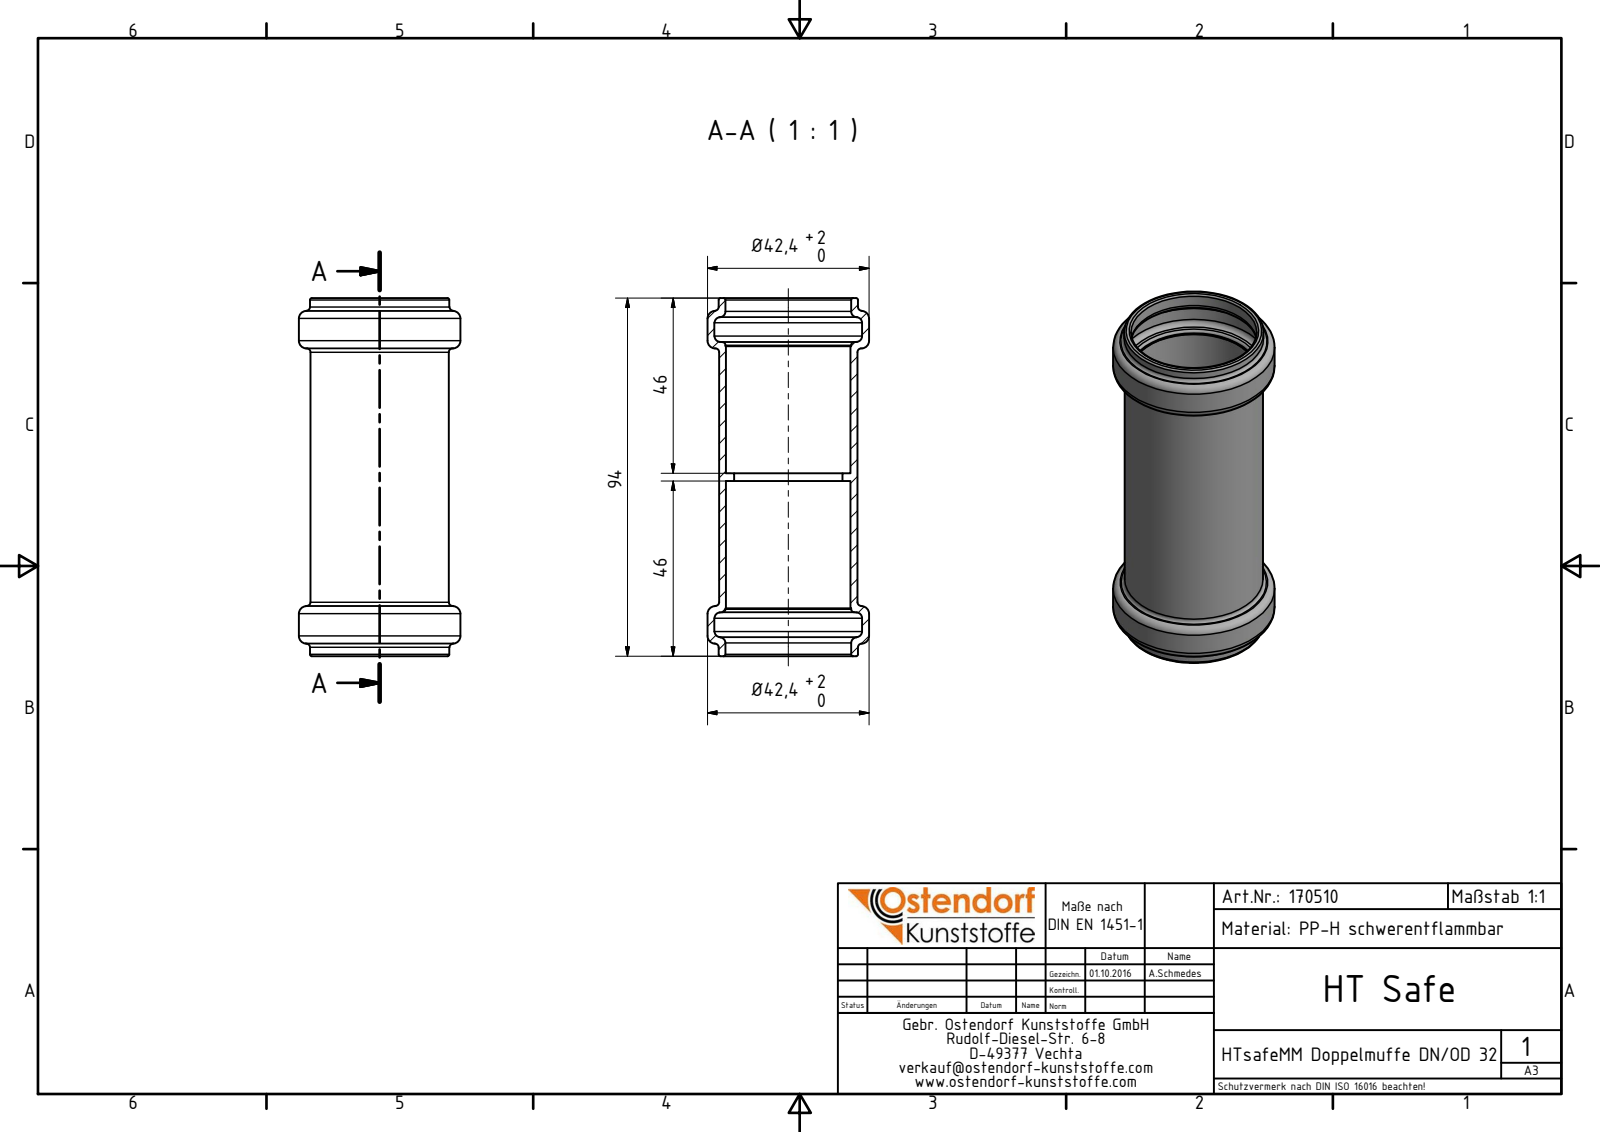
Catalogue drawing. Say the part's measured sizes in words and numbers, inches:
The part is named "170510 HTsafeMM DN_OD 32". Its 3-D file was written by "Autodesk Inventor 2016 (AUTOMOTIVE_DESIGN)". It is 1 solid with 48 faces: 6 planar, 14 cylindrical and 28 other. Overall it measures 3.701 by 1.669 by 1.669 inches. Its volume is 1.303 cubic inches and its surface area 36.13 square inches. Round holes: 1 of diameter 1.122, 1 of diameter 1.287, 1 of diameter 1.299, 1 of diameter 1.528. Round bosses or shafts: 1 of diameter 1.669, 1 of diameter 1.441, 1 of diameter 1.429. The main face-to-face distances are 0.079, 1.811, 1.89, 3.701, 0.497, 3.204, 1.314, 1.393, 2.706.
